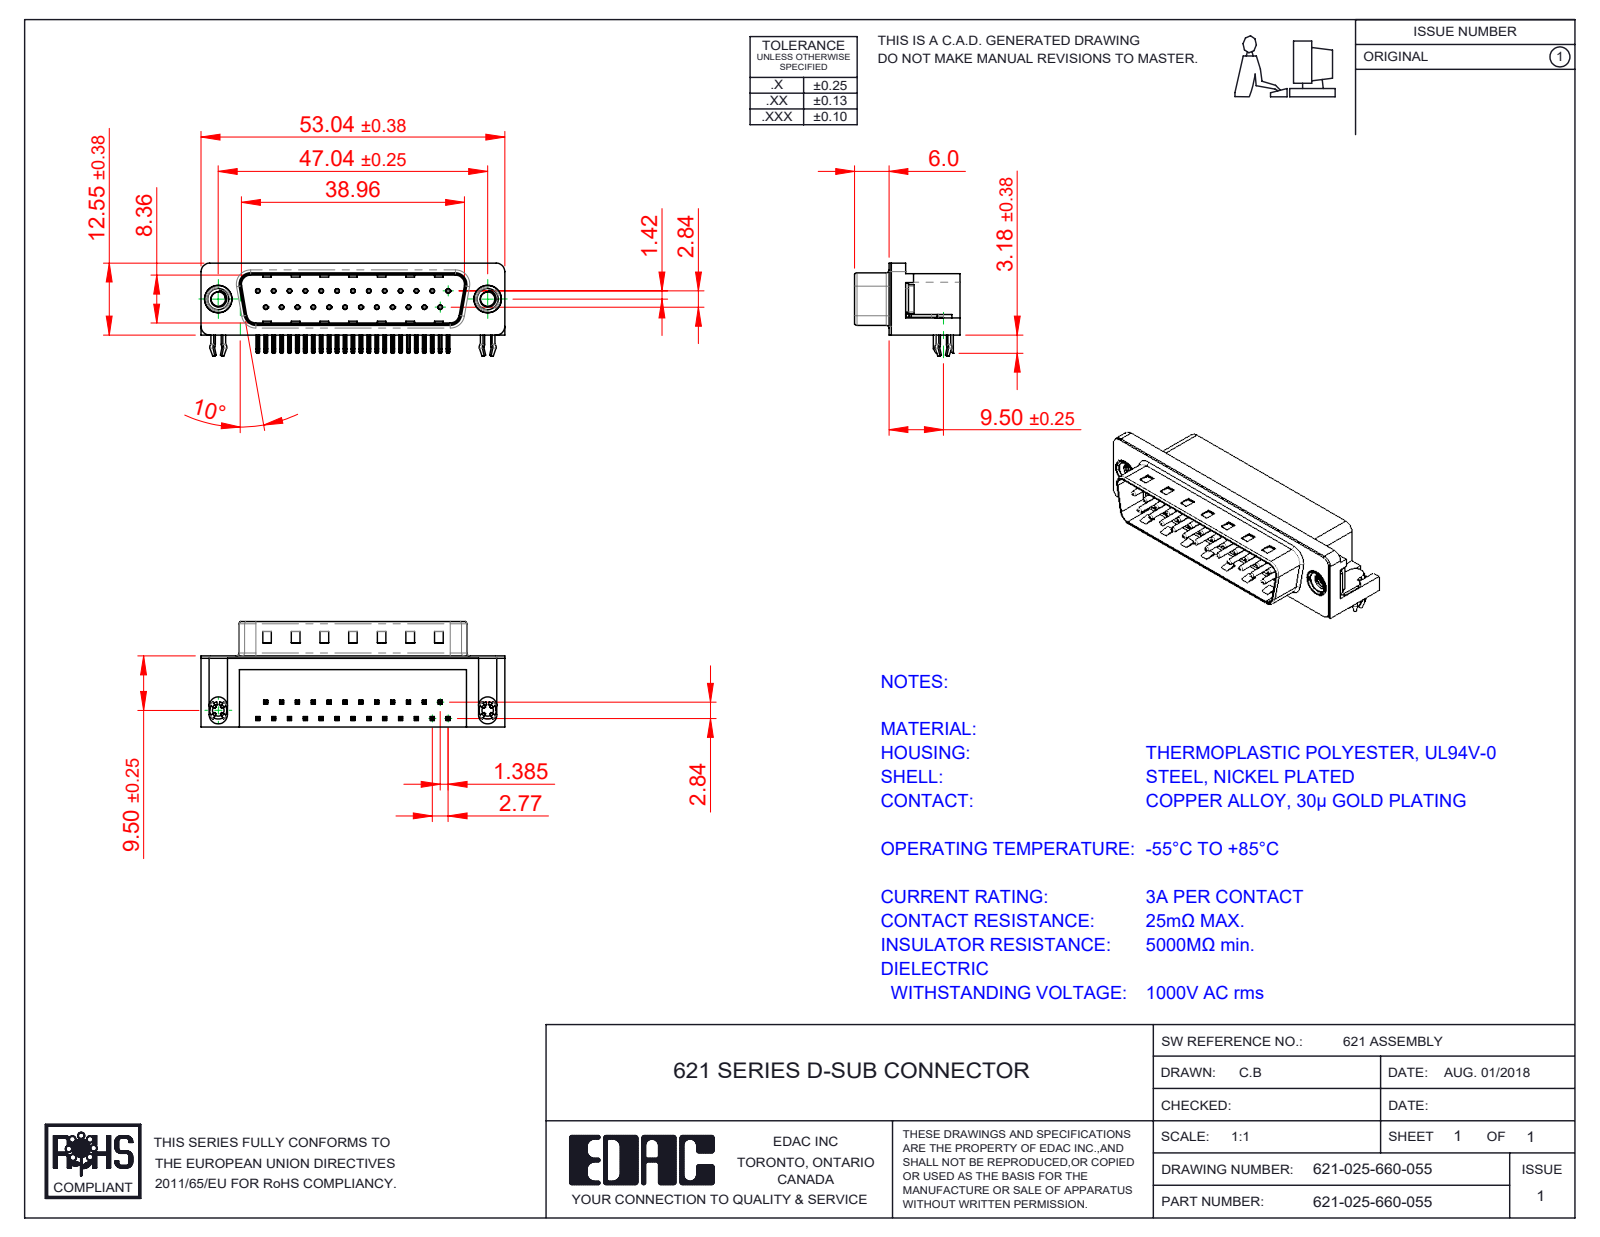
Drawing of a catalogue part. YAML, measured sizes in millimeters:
part_name: "621 Contact Bottom; 621 Shell_25 Socket; 621 M3 Threaded Rivet; 621 Contact Top (+3 more)"
step_written_by: "SolidWorks 2016 (CONFIG_CONTROL_DESIGN)"
units: millimeters
bodies: {solids: 31, faces: 2293, planar: 1405, cylindrical: 675, other: 213}
overall_size: [53.04, 18.4, 15.73]
volume: 6354
surface_area: 7765
round_holes:
  - {diameter: 0.35, count: 25}
  - {diameter: 0.8, count: 25}
  - {diameter: 2.26, count: 2}
  - {diameter: 2.5, count: 2}
  - {diameter: 4, count: 2}
  - {diameter: 4.8, count: 2}
  - {diameter: 5, count: 2}
round_bosses_or_shafts:
  - {diameter: 0.75, count: 25}
  - {diameter: 4.9, count: 2}
  - {diameter: 4.75, count: 2}
  - {diameter: 3.9, count: 2}
  - {diameter: 3.26, count: 2}
partial_cylinders:
  - {radius: 0.25, count: 108}
  - {radius: 0.12, count: 50}
  - {radius: 1, count: 16}
  - {radius: 0.5, count: 9}
  - {radius: 1.6, count: 8}
  - {radius: 1.5, count: 7}
  - {radius: 0.9, count: 4}
  - {radius: 2, count: 4}
face_to_face_distances: [0.4, 12, 10.35, 2.1, 8.76, 10.46, 1.7, 10.86, 12.4, 9]
hole_center_spacings: [3.16, 2.77, 5.54, 8.31, 11.08, 13.85, 16.62, 5.03]
